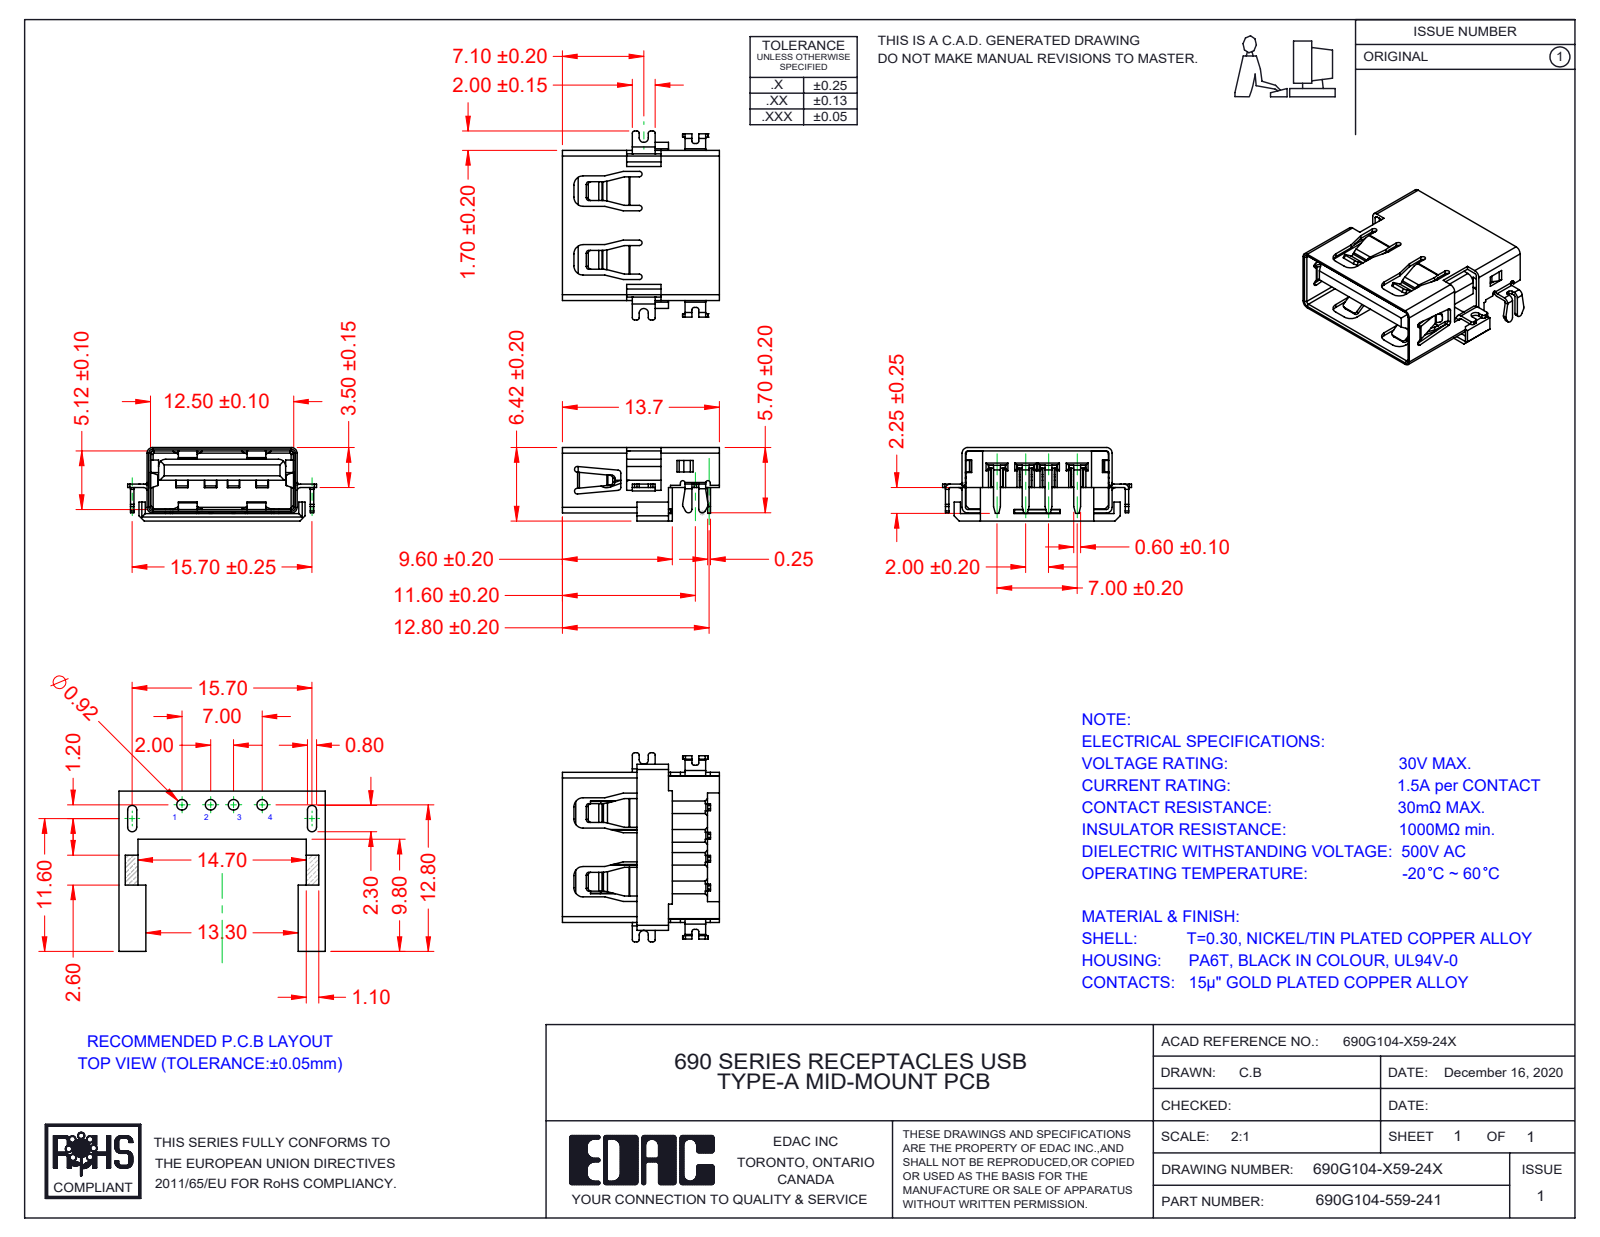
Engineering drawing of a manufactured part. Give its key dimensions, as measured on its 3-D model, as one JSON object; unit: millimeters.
{"part_name": "Contacts 690G104-X59-24X; 690G104-159-241; Insulator 690G104-X59-24X_Black; Shell 690G104-X59-24X", "step_written_by": "SolidWorks 2020 (AUTOMOTIVE_DESIGN)", "units": "millimeters", "bodies": {"solids": 6, "faces": 800, "planar": 585, "cylindrical": 185, "other": 30}, "overall_size": [16.5, 13.7, 6.42], "volume_mm3": 417, "surface_area_mm2": 1719, "partial_cylinders_radius": [[0.2, 30], [0.25, 21], [0.1, 12], [0.5, 12], [0.3, 8], [0.4, 7], [0.8, 6], [0.15, 3]], "face_to_face_distances": [5.42, 2.86, 2.56, 0.72, 4.7, 2.5, 1.02, 5.12, 5.72, 4.4]}
